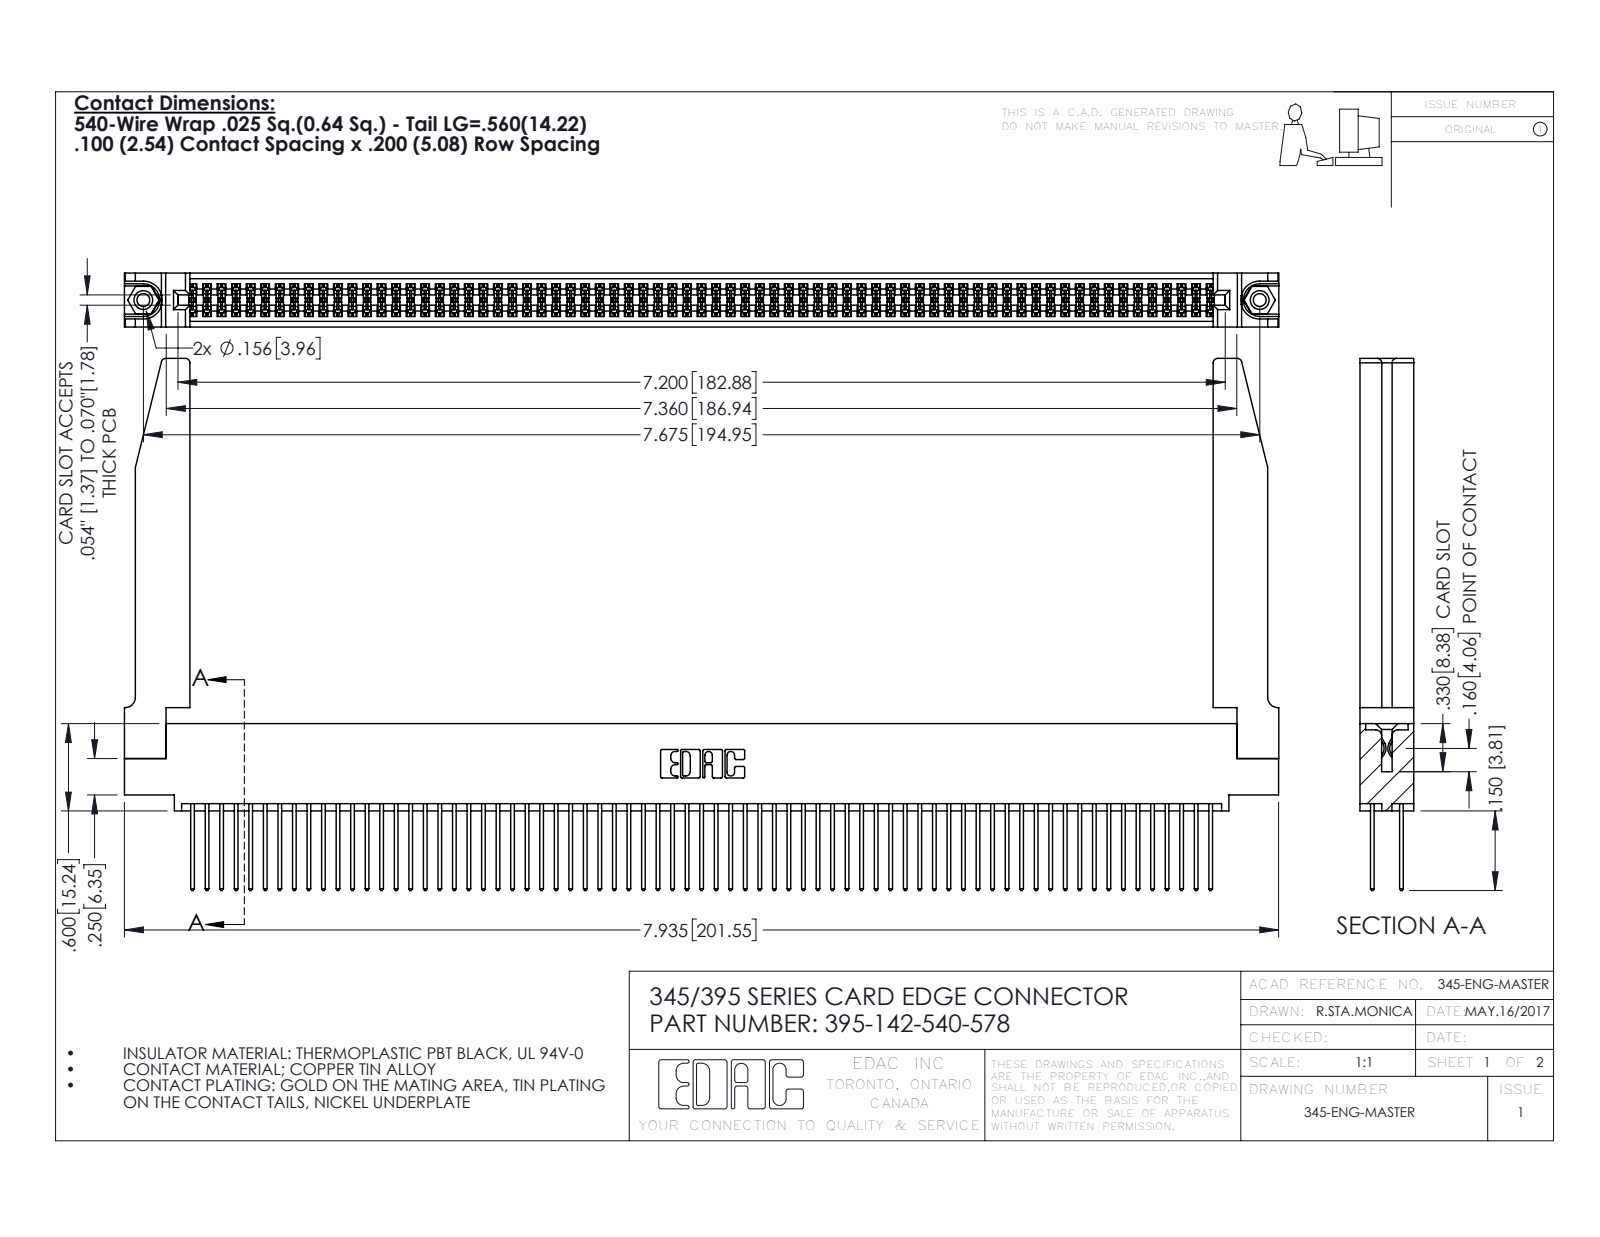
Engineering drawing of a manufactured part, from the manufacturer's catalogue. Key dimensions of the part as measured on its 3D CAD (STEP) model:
Part name (STEP PRODUCT): 345-292-001_345-293-140; 345-220-078_345-220-078; 395-142-540-578; 345-250-001_345-250-001-102 (+1 more)
STEP written by: SolidWorks 2016 (CONFIG_CONTROL_DESIGN)
Units: inches
Bodies: 147 solids, 7464 faces (4912 planar, 2500 cylindrical, 52 other)
Overall size (bounding box): 7.936 × 3.657 × 0.37
Volume: 1.714 in³ · Surface area: 62.03 in²
Round holes (diameter × count): ⌀0.089 ×2, ⌀0.125 ×2, ⌀0.156 ×2, ⌀0.064 ×1
Round bosses / shafts (diameter × count): ⌀0.155 ×2
Partial cylindrical surfaces — rounded edges, fillets, slot ends (radius × count): R0.006 ×213, R0.01 ×142, R0.01 ×22, R0.03 ×8, R0.007 ×6, R0.031 ×6, R0.026 ×3, R0.014 ×2
Main face-to-face distances: 0.072, 0.298, 0.37, 0.098, 0.272, 0.025, 0.2, 0.225, 0.175, 0.149
Hole centre spacings: 0.27, 7.439, 7.675
